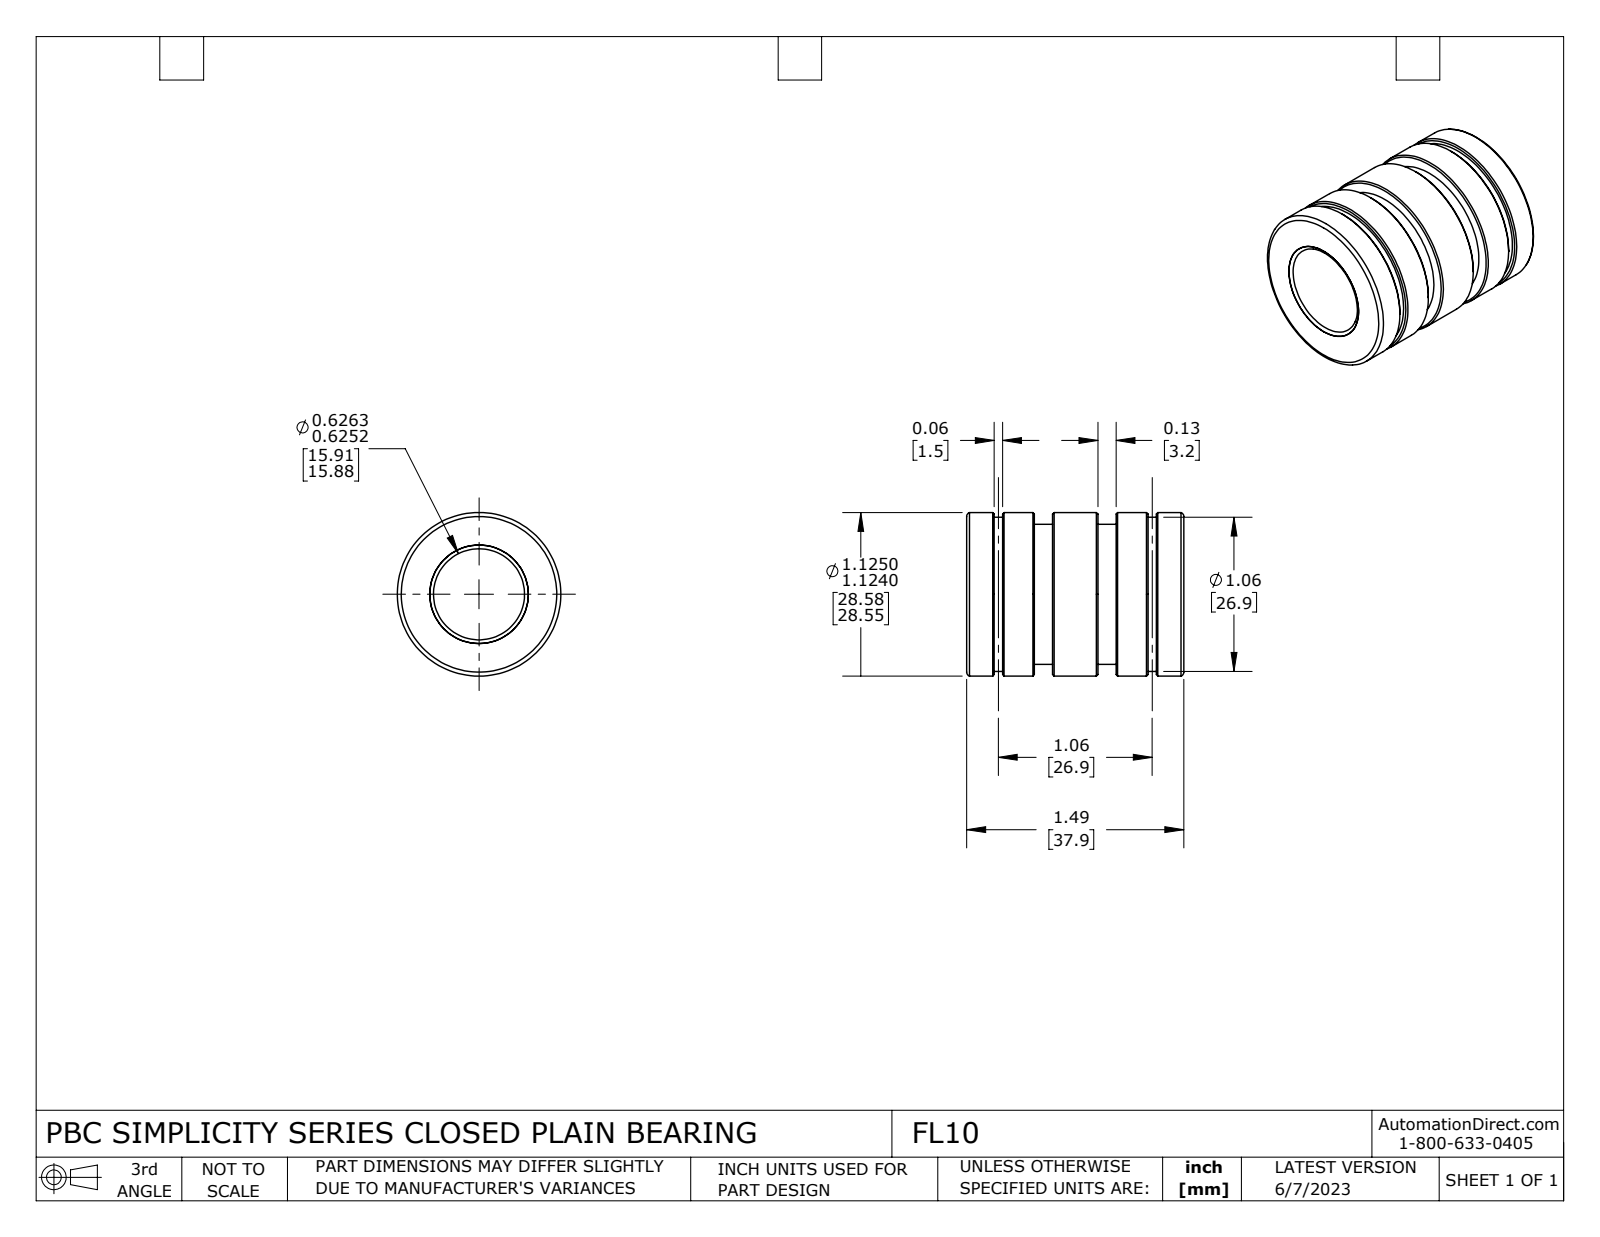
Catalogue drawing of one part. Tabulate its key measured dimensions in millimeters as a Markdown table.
| quantity | value |
| --- | --- |
| part name | FL10 |
| STEP written by | SolidWorks 2021 (CONFIG_CONTROL_DESIGN) |
| units | millimeters |
| bodies | 2 solids, 58 faces (10 planar, 24 cylindrical, 24 other) |
| overall size | 37.9 × 28.5 × 28.5 |
| volume | 15 400 mm³ |
| surface area | 10 960 mm² |
| round holes (diameter × count) | 15.9 × 1, 17.2 × 1 |
| round bosses / shafts (diameter × count) | 28.5 × 1, 26.9 × 1, 24.4 × 1 |
| main face-to-face distances | 37.9, 15, 22.9, 11.8, 26.1, 3.2, 11.1, 7.9, 14.3, 6.2 |
